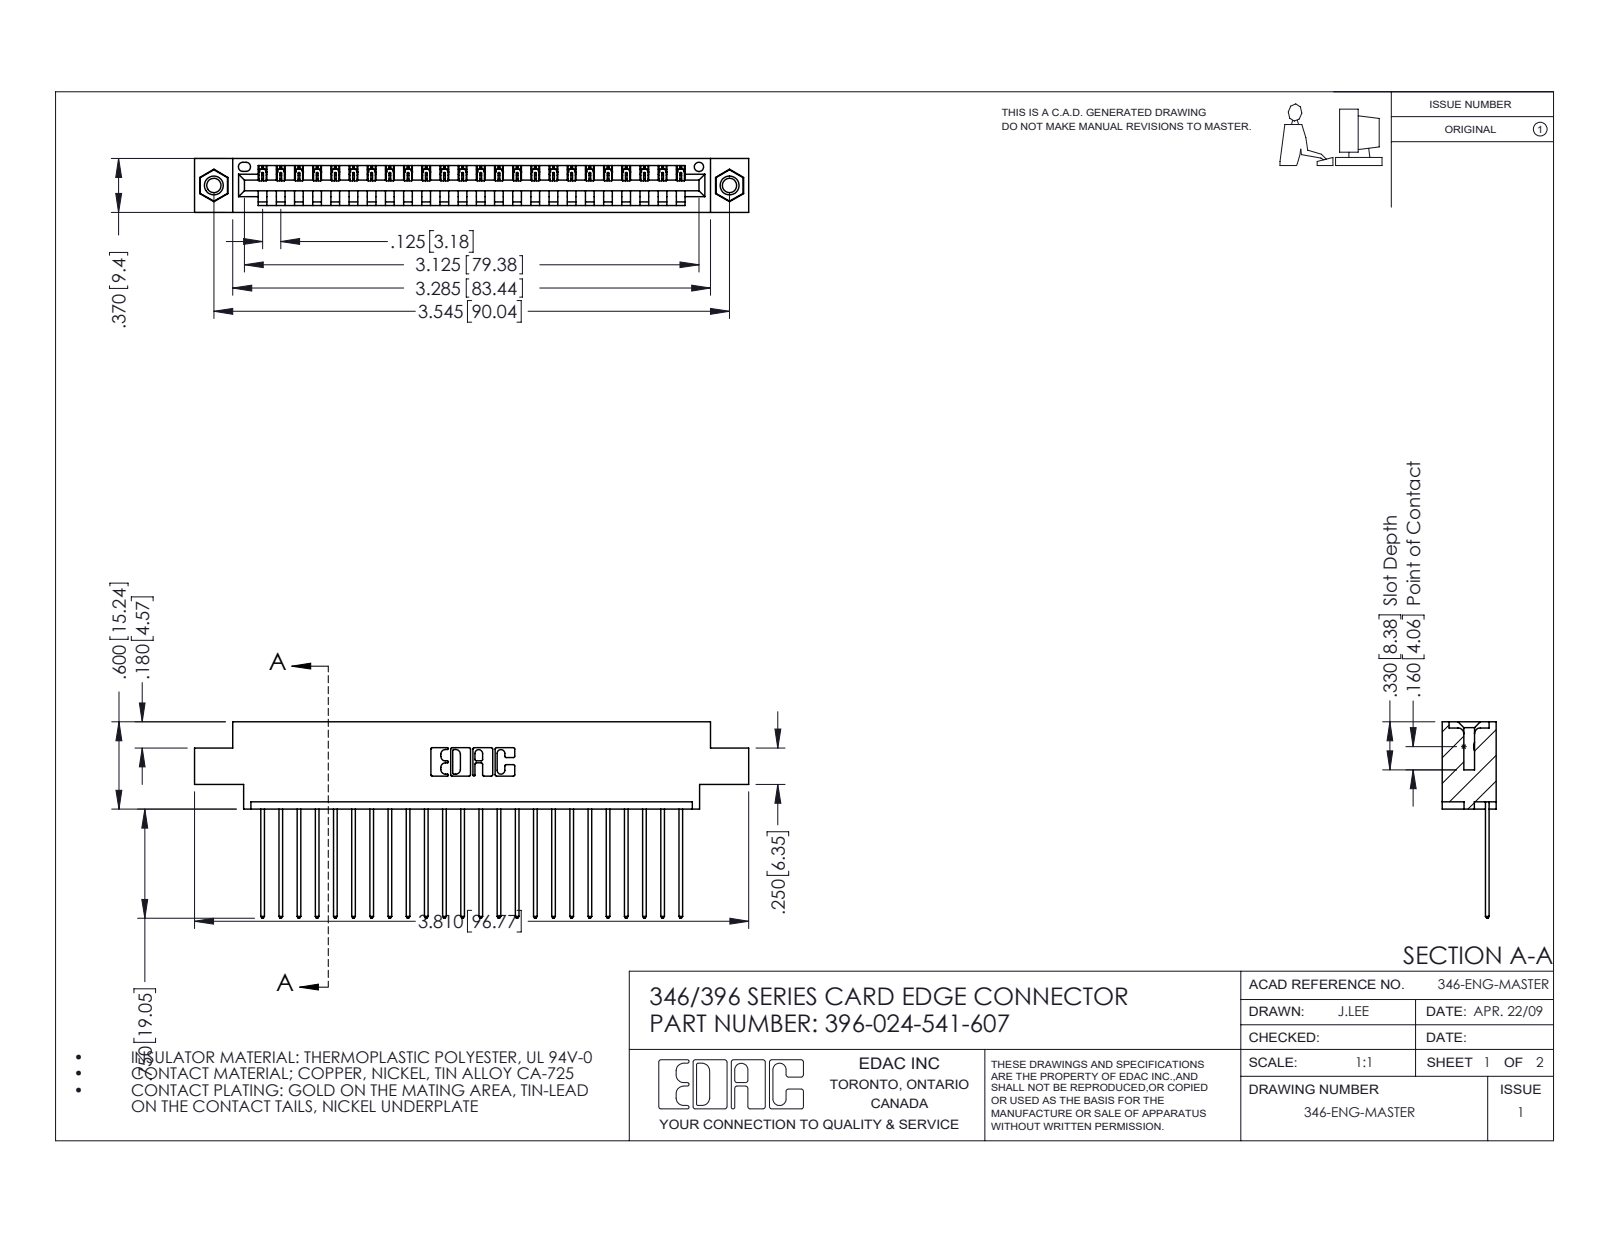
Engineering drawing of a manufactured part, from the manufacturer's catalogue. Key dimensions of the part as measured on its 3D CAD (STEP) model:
Part name (STEP PRODUCT): 345-250-001_345-250-005-103; 345-292-001_345-293-141; 396-024-541-607; 346 Part_0.170 Offset - 0.156 Dia-TI
STEP written by: SolidWorks 2016 (CONFIG_CONTROL_DESIGN)
Units: inches
Bodies: 27 solids, 1578 faces (1072 planar, 490 cylindrical, 16 other)
Overall size (bounding box): 3.81 × 1.35 × 0.37
Volume: 0.552 in³ · Surface area: 18.27 in²
Round holes (diameter × count): ⌀0.098 ×2, ⌀0.125 ×2, ⌀0.156 ×2, ⌀0.064 ×1
Round bosses / shafts (diameter × count): ⌀0.155 ×2
Partial cylindrical surfaces — rounded edges, fillets, slot ends (radius × count): R0.006 ×48, R0.01 ×48, R0.01 ×22, R0.007 ×6, R0.031 ×6, R0.026 ×3, R0.031 ×2, R0.04 ×2
Main face-to-face distances: 0.048, 0.322, 0.37, 0.25, 0.072, 0.298, 0.025, 0.222, 0.148, 0.1
Hole centre spacings: 0.246, 3.337, 3.545
